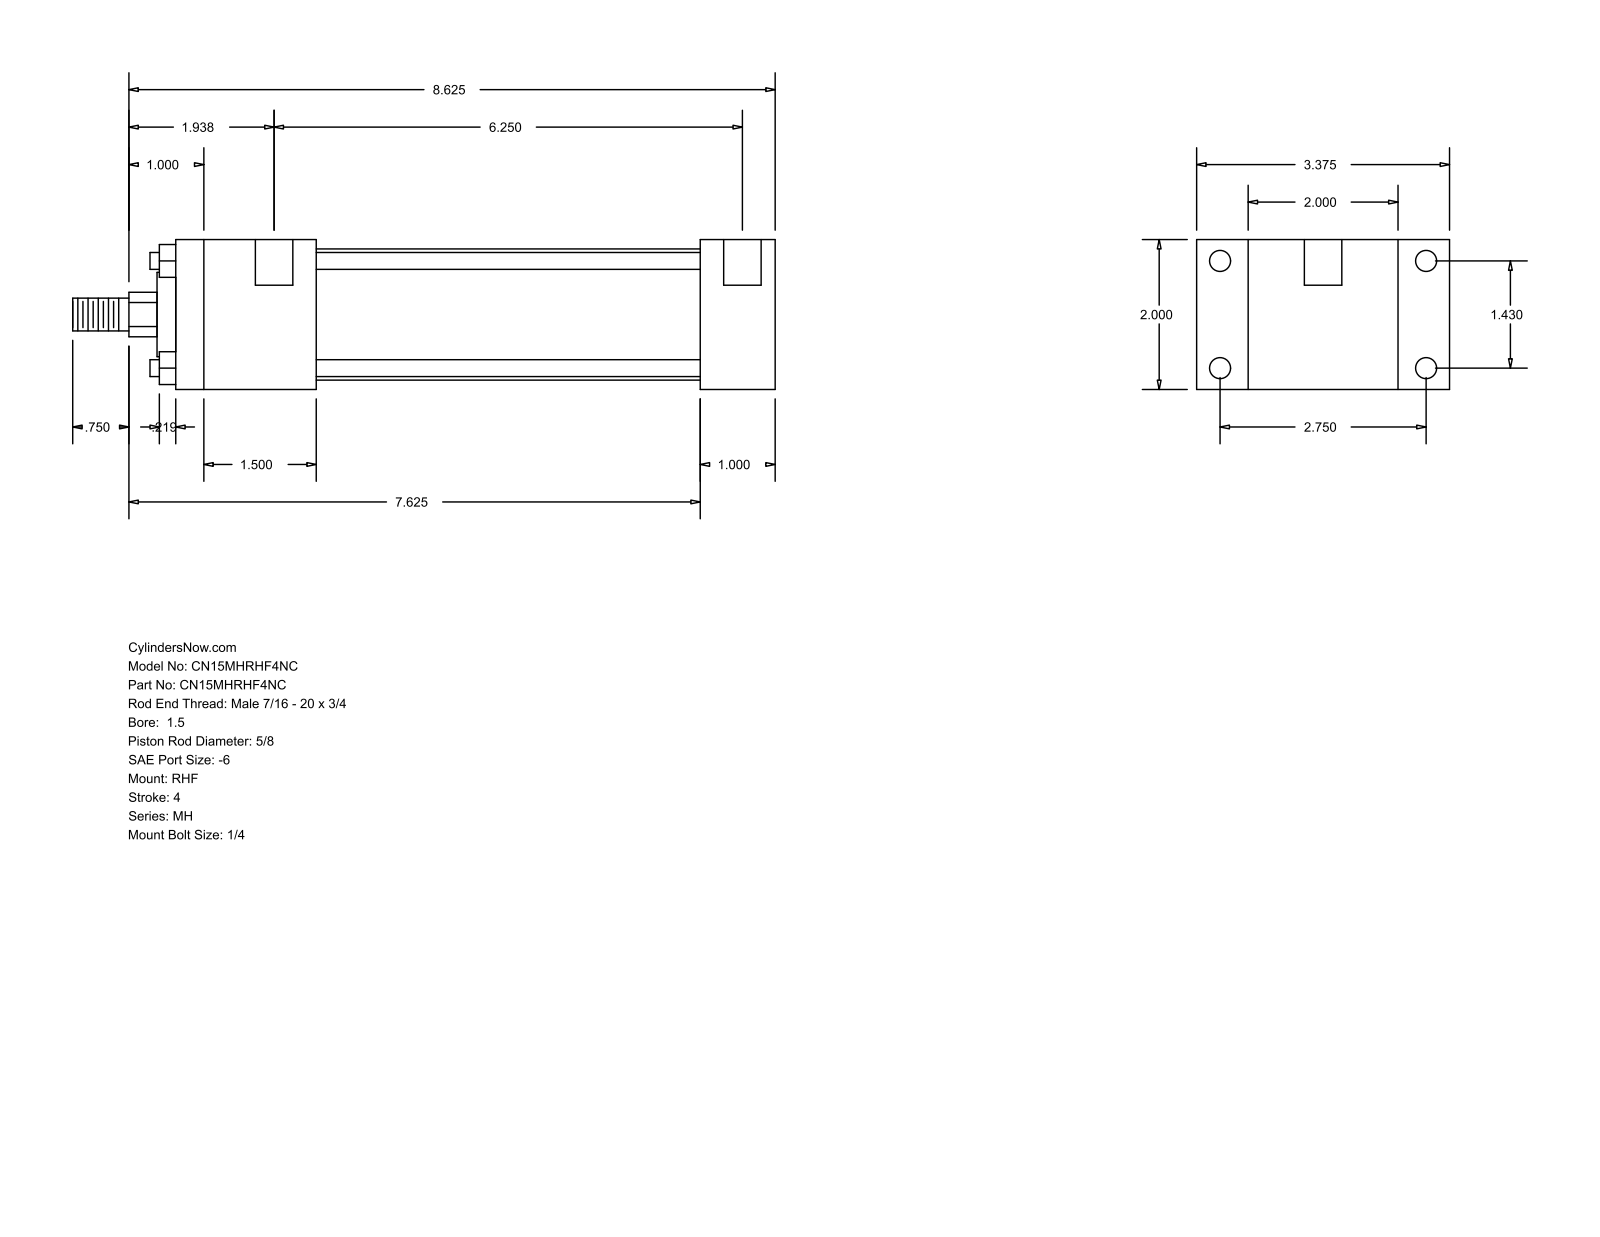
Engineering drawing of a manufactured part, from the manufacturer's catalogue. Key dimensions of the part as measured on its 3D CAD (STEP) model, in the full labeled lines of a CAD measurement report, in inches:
Part name (STEP PRODUCT): MH_RHF__0150_0.625
STEP written by: GSSL Pune (CONFIG_CONTROL_DESIGN)
Units: inches
Bodies: 0 solids, 88 faces (60 planar, 28 cylindrical, 0 other)
Overall size (bounding box): 9.375 × 3.375 × 2
Round holes (diameter × count): ⌀0.219 ×4, ⌀0.281 ×4, ⌀0.5 ×2
Round bosses / shafts (diameter × count): ⌀0.225 ×4, ⌀1.75 ×1, ⌀1.125 ×1, ⌀0.625 ×1, ⌀0.437 ×1
Partial cylindrical surfaces — rounded edges, fillets, slot ends (radius × count): R0.297 ×1
Main face-to-face distances: 2, 0.687, 2.687, 1, 7, 8, 3.375, 1.875, 5.125, 6.125
Hole centre spacings: 1.43, 2.75, 3.099, 6.375, 0.125, 6.25
